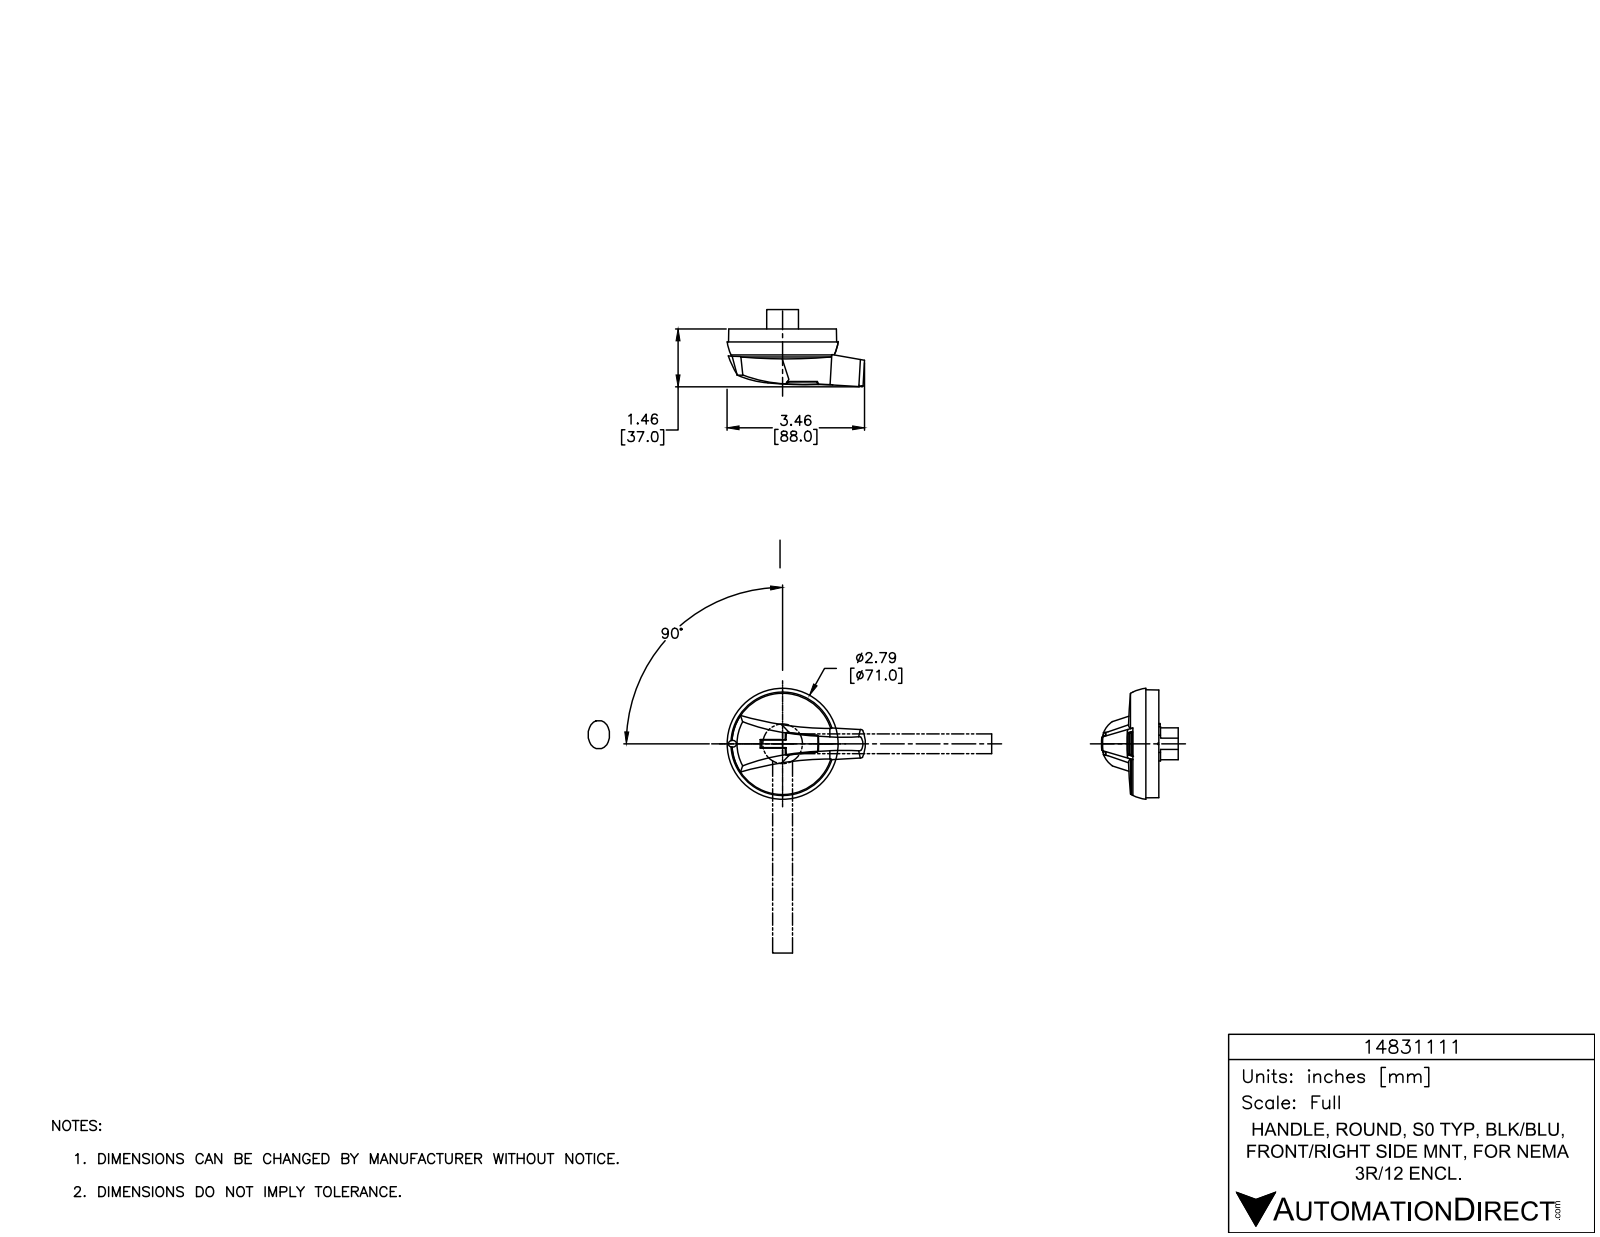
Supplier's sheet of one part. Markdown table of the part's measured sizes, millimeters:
| quantity | value |
| --- | --- |
| part name | 14831111 |
| STEP written by | SolidWorks 2015 (AUTOMOTIVE_DESIGN) |
| units | millimeters |
| bodies | 5 solids, 1981 faces (411 planar, 317 cylindrical, 1253 other) |
| overall size | 88.4 × 71.1 × 48.9 |
| volume | 53 420 mm³ |
| surface area | 57 490 mm² |
| round holes (diameter × count) | 4.3 × 4, 4.9 × 4, 10 × 4, 2 × 3, 3.3 × 2, 4 × 2, 8.5 × 2, 3 × 1, 3.2 × 1, 11.6 × 1, 66.5 × 1 |
| round bosses / shafts (diameter × count) | 65 × 1 |
| partial cylindrical surfaces (radius × count) | 0.5 × 96, 0.3 × 19, 1 × 11, 0.3 × 10, 0.8 × 8, 3.6 × 4, 4.7 × 4, 0.4 × 1 |
| main face-to-face distances | 1.5, 1.8, 3.3, 15.6, 1.3, 0.8, 14.1, 12.3, 3.9, 7.5 |
| hole center spacings | 14.3, 24.4, 39.5, 30, 17, 17.2, 21.4, 28 |
